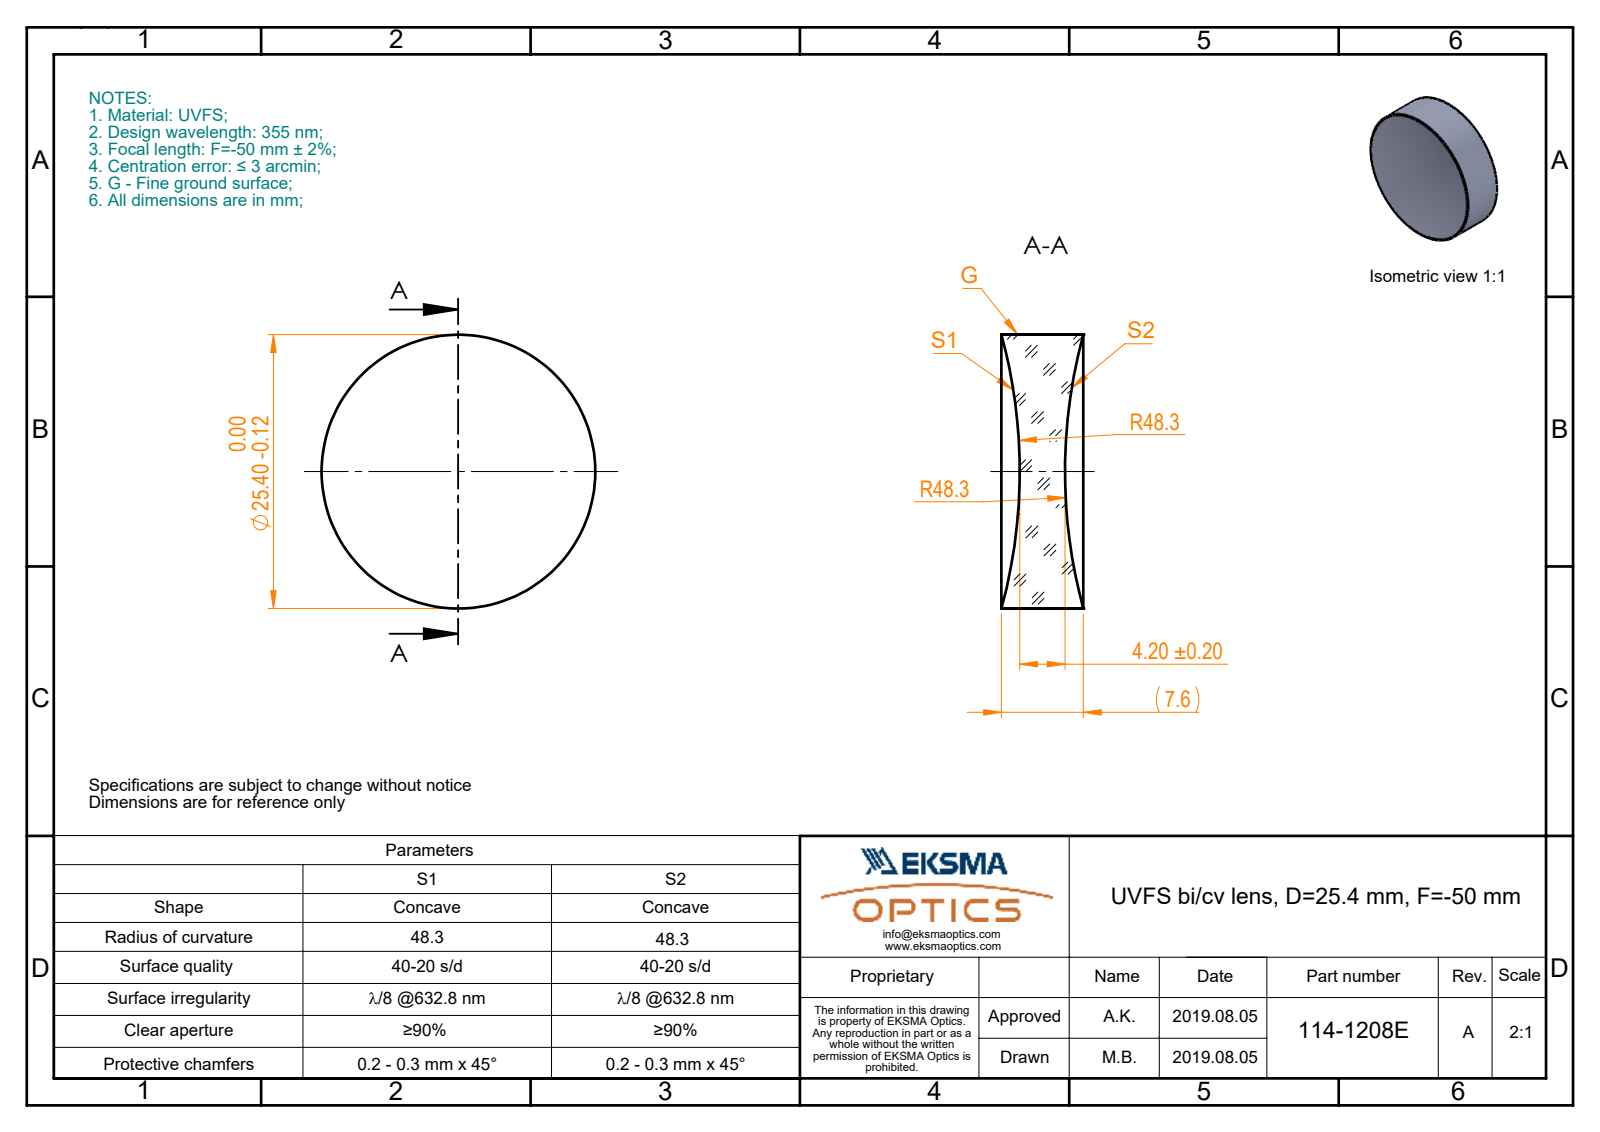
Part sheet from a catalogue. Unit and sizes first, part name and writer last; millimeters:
Units: millimetres
Overall size (bounding box): 25.4 × 25.4 × 7.6
Round bosses / shafts (diameter × count): ⌀25.4 ×1
Volume: 2 985 mm³ · Surface area: 1 638 mm²
Bodies: 1 solid, 6 faces (0 planar, 2 cylindrical, 4 other)
Part name (STEP PRODUCT): 114-1208E UVFS bi-cv 25.4 F-50
STEP written by: SolidWorks 2017 (CONFIG_CONTROL_DESIGN)
